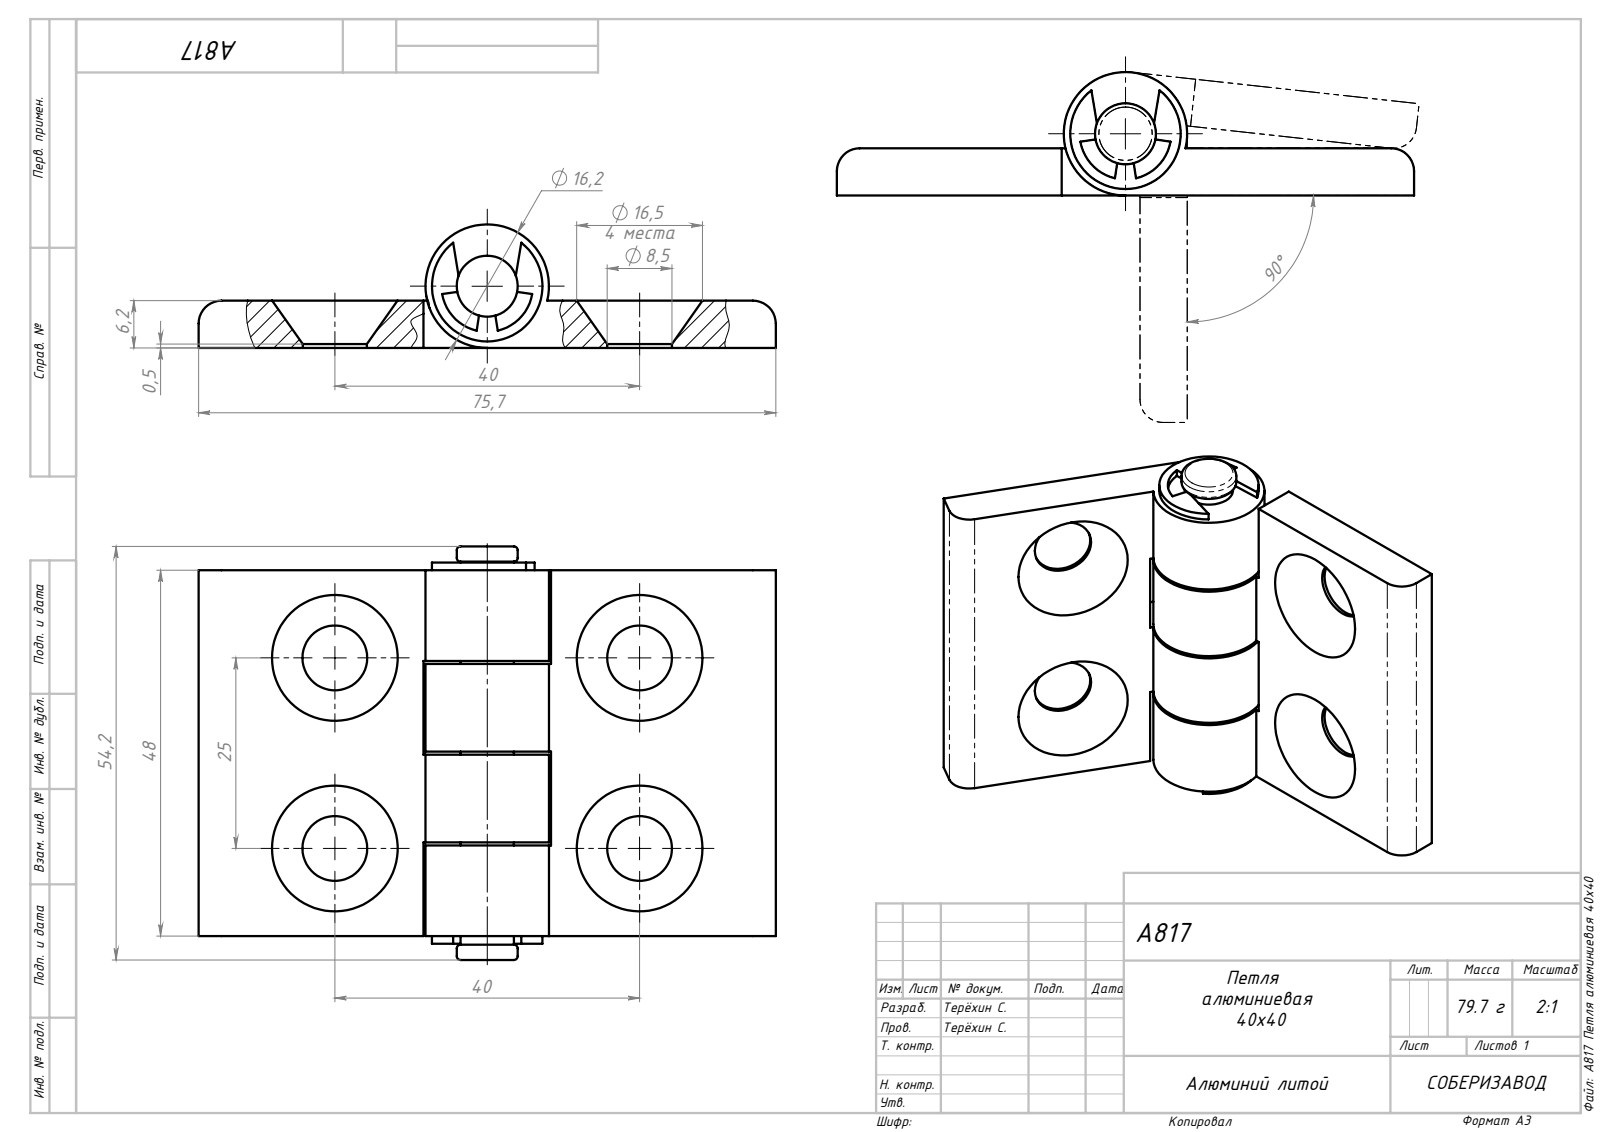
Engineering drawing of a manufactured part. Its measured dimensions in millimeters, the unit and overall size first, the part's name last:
Units: millimetres
Overall size (bounding box): 75.75 × 54.25 × 16.2
Round holes (diameter × count): ⌀8.5 ×4, ⌀7 ×1
Round bosses / shafts (diameter × count): ⌀16.2 ×1, ⌀14.5 ×1, ⌀8 ×1
Partial cylindrical surfaces — rounded edges, fillets, slot ends (radius × count): R3 ×2, R6 ×1
Main face-to-face distances: 6.2, 11.9, 12.3, 23.8, 48, 24.2, 0.4, 35.7, 36.1, 11.5
Hole centre spacings: 25, 40, 47.17
Volume: 25 200 mm³ · Surface area: 13 729 mm²
Bodies: 5 solids, 104 faces (38 planar, 50 cylindrical, 16 other)
Part name (STEP PRODUCT): A817 Петля, часть 40 серии_00; A817 Палец_00; A817 Кольцо_00; A817 Петля алюминиевая 40х40
STEP written by: SolidWorks 2022 (AUTOMOTIVE_DESIGN)
